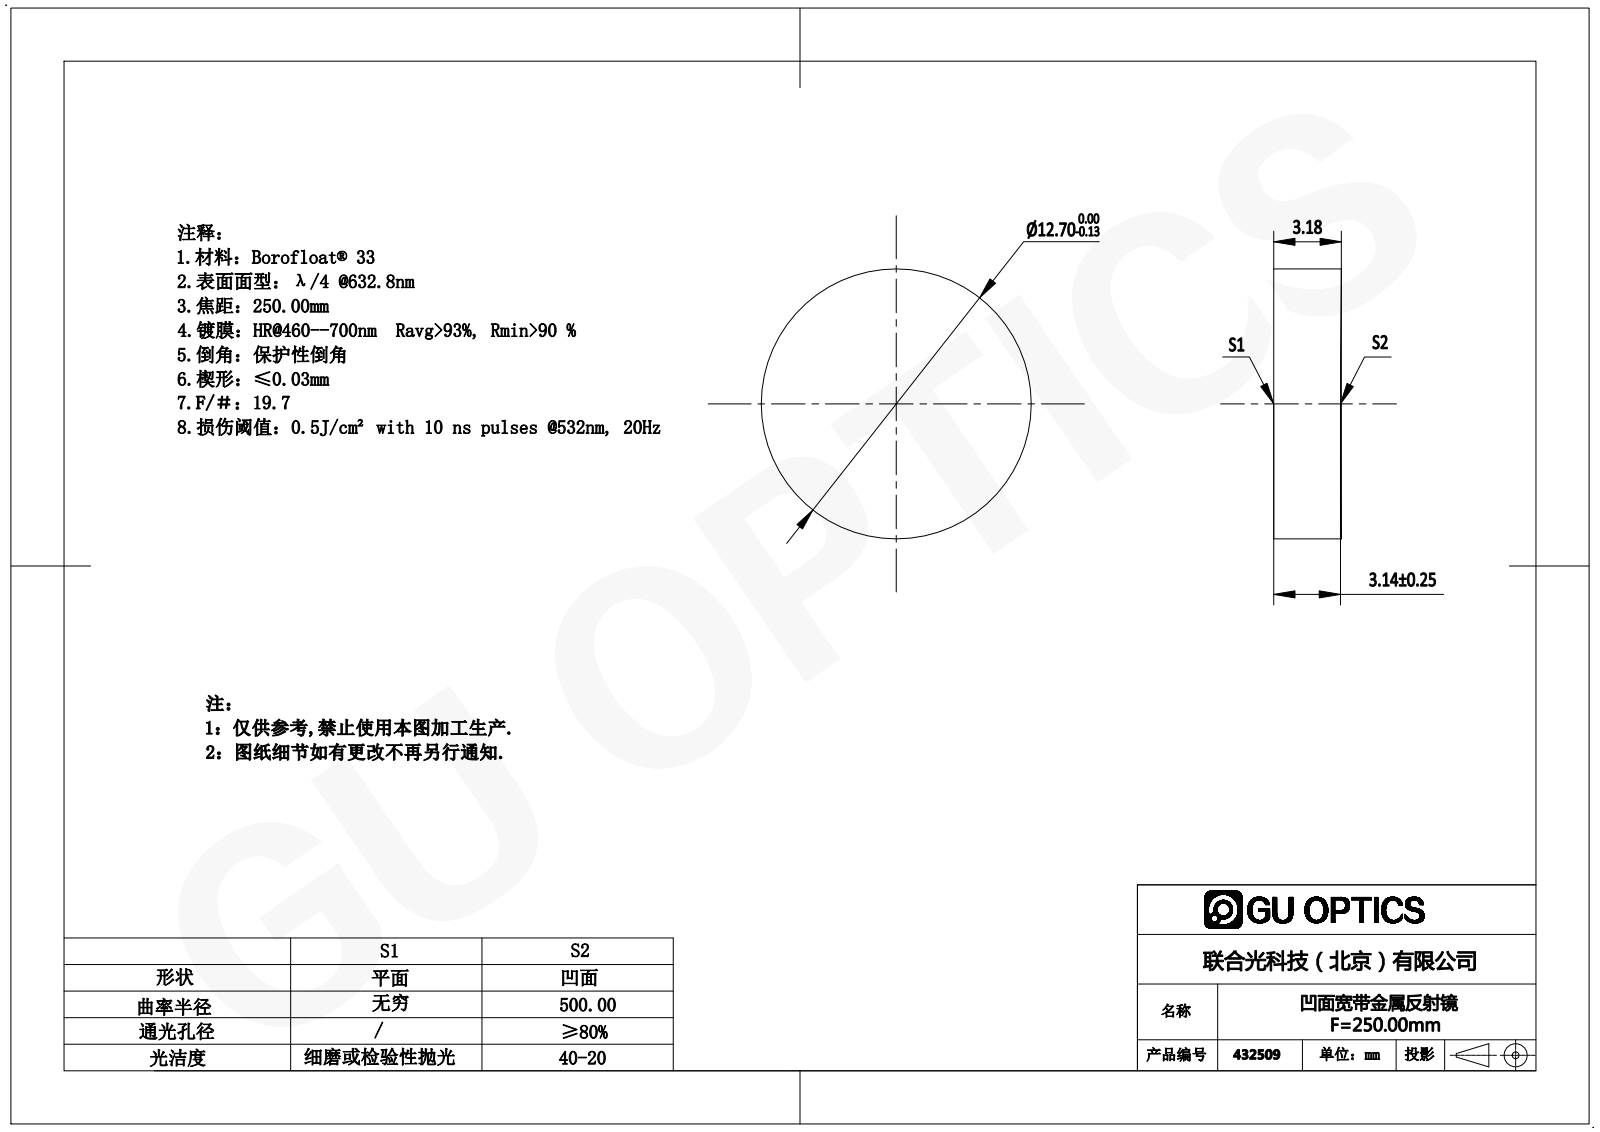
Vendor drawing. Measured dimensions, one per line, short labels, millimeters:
name: 432504
written by: SolidWorks 2016 (AUTOMOTIVE_DESIGN)
unit: mm
bodies: 1 solid, 5 faces (1 planar, 2 cylindrical, 2 other)
size: 12.7 × 12.7 × 3.18
volume: 400 mm³; area: 380 mm²
bosses: 1× ⌀12.7
